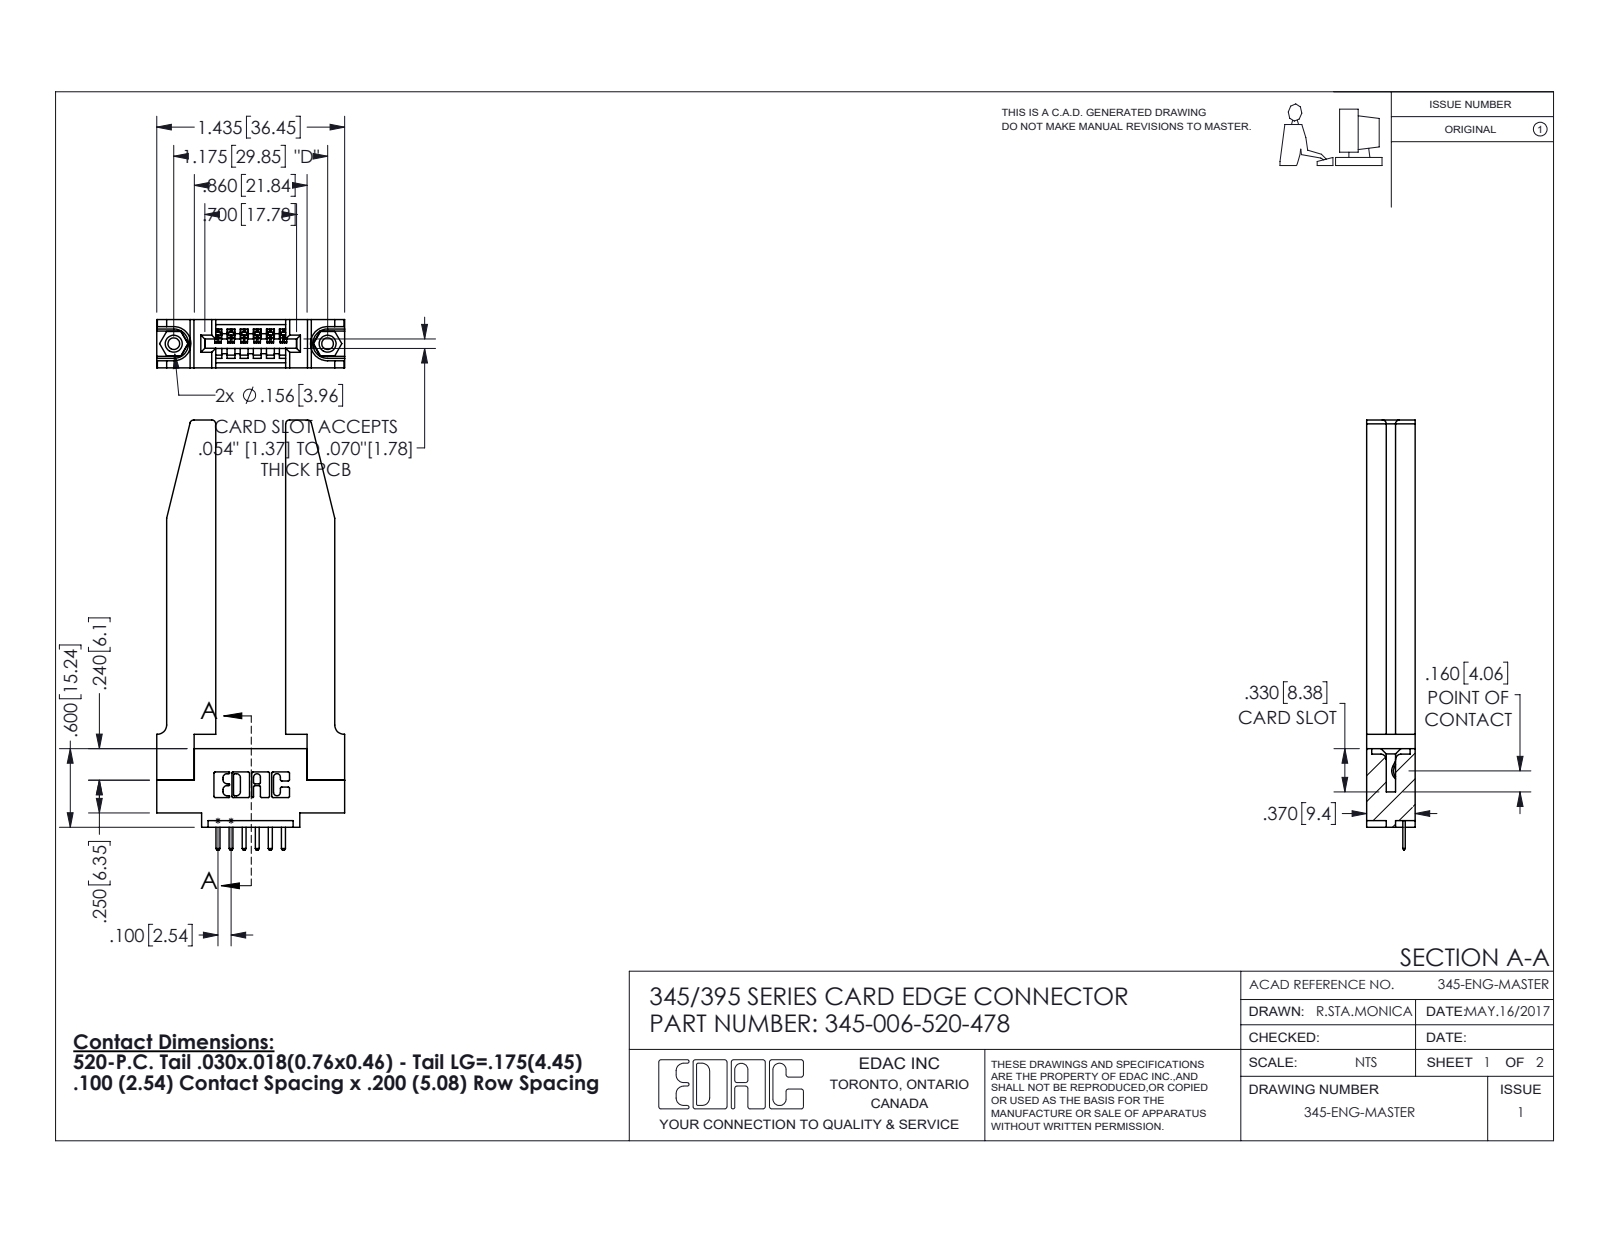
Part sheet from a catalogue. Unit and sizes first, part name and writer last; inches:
Units: inches
Overall size (bounding box): 3.285 × 1.436 × 0.37
Round holes (diameter × count): ⌀0.089 ×2, ⌀0.125 ×2, ⌀0.156 ×2, ⌀0.064 ×1
Round bosses / shafts (diameter × count): ⌀0.155 ×2
Partial cylindrical surfaces — rounded edges, fillets, slot ends (radius × count): R0.01 ×22, R0.01 ×14, R0.006 ×12, R0.03 ×8, R0.007 ×6, R0.031 ×6, R0.026 ×3, R0.031 ×2
Main face-to-face distances: 0.37, 0.15, 0.22, 0.535, 0.072, 0.148, 0.298, 0.077, 0.071, 0.055
Hole centre spacings: 0.27, 0.946, 1.175
Volume: 0.662 in³ · Surface area: 16.23 in²
Bodies: 11 solids, 736 faces (478 planar, 206 cylindrical, 52 other)
Part name (STEP PRODUCT): 345 Part_0.110 Offset - 0.156 Dia-TH; 345-250-001_345-250-001-102; 345-292-001_345-293-120; 345-006-520-478 (+1 more)
STEP written by: SolidWorks 2016 (CONFIG_CONTROL_DESIGN)
